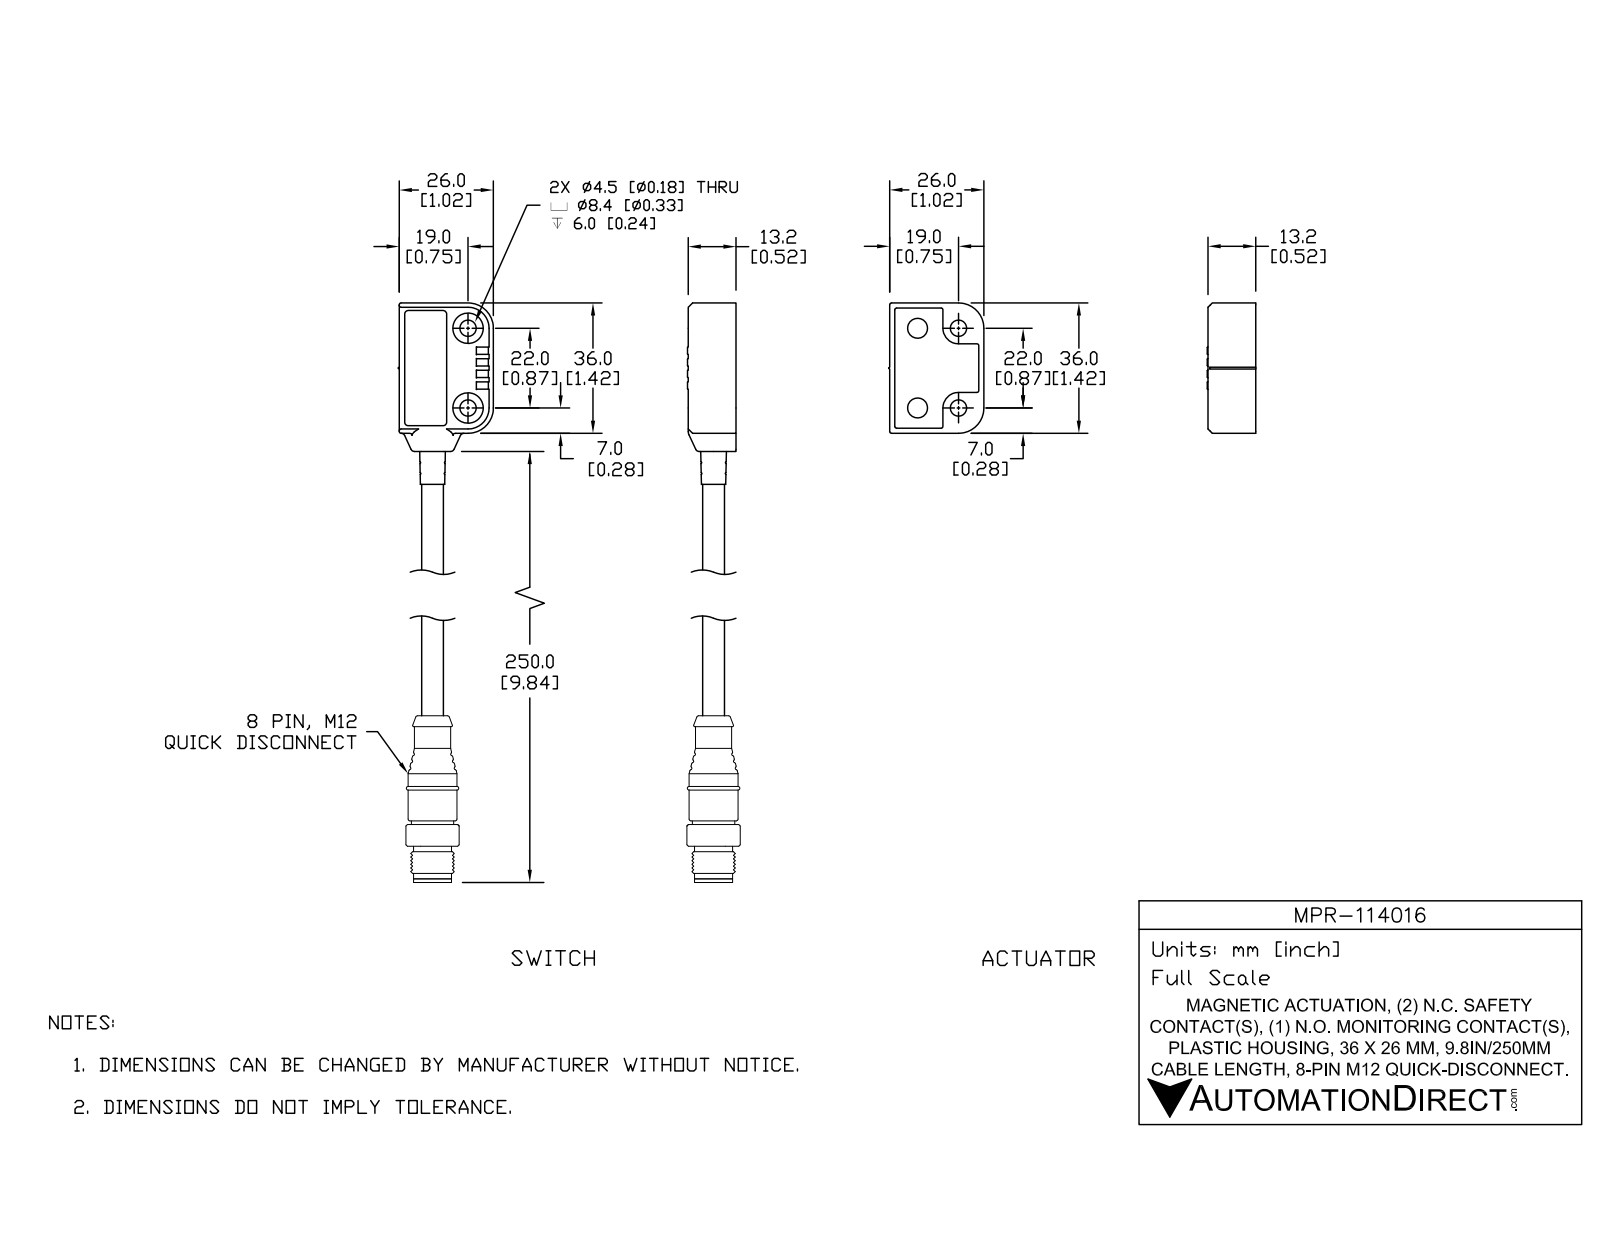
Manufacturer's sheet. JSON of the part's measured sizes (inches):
{"part_name": "MPR-114016_2; MPR-114016; MPR-114016_1", "step_written_by": "SolidWorks 2017 (AUTOMOTIVE_DESIGN)", "units": "inches", "bodies": {"solids": 10, "faces": 1476, "planar": 650, "cylindrical": 441, "other": 385}, "overall_size": [11.457, 2.087, 0.579], "volume_in3": 1.44, "surface_area_in2": 36.96, "round_holes": [[0.177, 4], [0.331, 4], [0.195, 2], [0.197, 1], [0.232, 1], [0.276, 1], [0.327, 1], [0.465, 1]], "round_bosses_or_shafts": [[0.031, 8], [0.079, 3], [0.197, 2], [0.091, 2], [0.531, 1], [0.461, 1], [0.413, 1], [0.394, 1]], "partial_cylinders_radius": [[0.02, 85], [0.008, 30], [0.012, 28], [0.004, 17], [0.039, 13], [0.169, 4], [0.201, 4], [0.276, 4]], "face_to_face_distances": [0.055, 0.461, 0.453, 0.39, 1.063, 0.047, 0.059, 0.094, 0.445, 0.5], "hole_center_spacings": [0.866, 0.445, 0.974, 1.091, 1.393, 1.535, 1.763, 0.396]}
